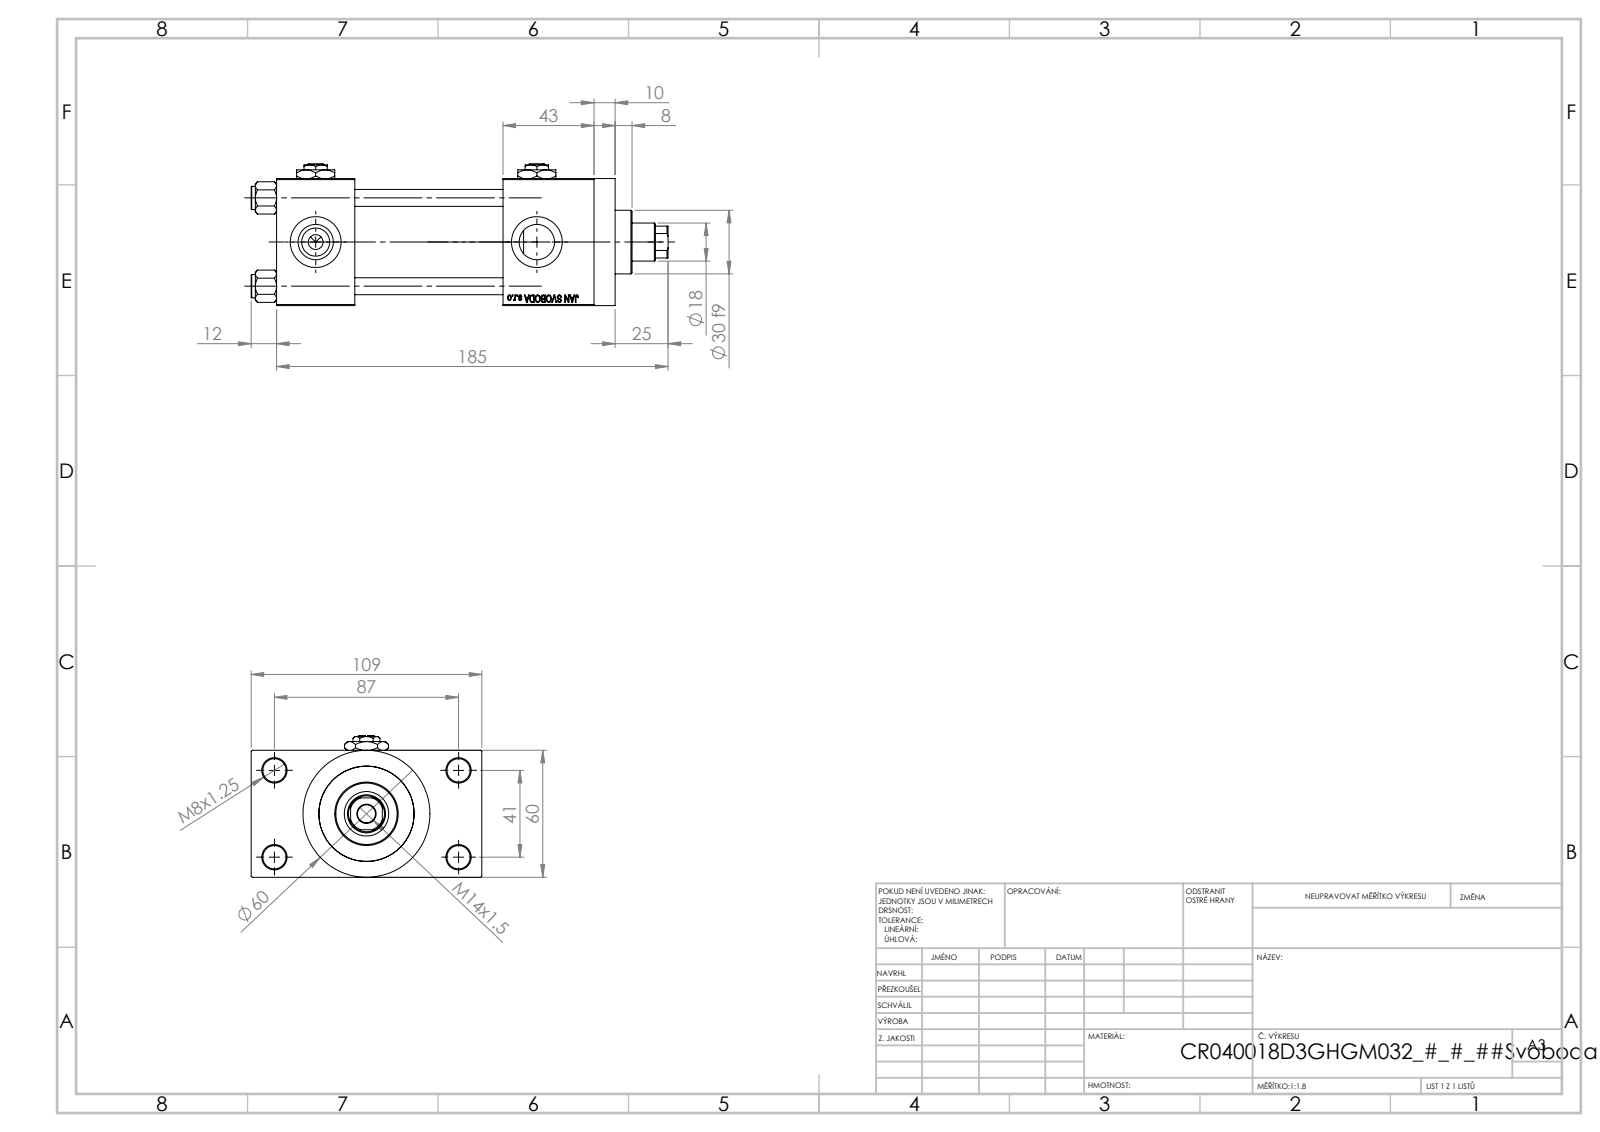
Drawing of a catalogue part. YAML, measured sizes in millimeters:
part_name: "V215_VC_A; NUT_M5_D; V215CR_D_TYCINKA; V215CR_VCP_D (+2 more)"
step_written_by: "SolidWorks 2019 (CONFIG_CONTROL_DESIGN)"
units: millimeters
bodies: {solids: 13, faces: 1205, planar: 546, cylindrical: 99, other: 560}
overall_size: [197, 109, 67]
volume: 520667
surface_area: 130319
round_holes:
  - {diameter: 8, count: 4}
  - {diameter: 11, count: 4}
  - {diameter: 16.66, count: 4}
  - {diameter: 24, count: 4}
  - {diameter: 7, count: 3}
  - {diameter: 8.5, count: 1}
  - {diameter: 18, count: 1}
  - {diameter: 21, count: 1}
  - {diameter: 31, count: 1}
  - {diameter: 40, count: 1}
  - {diameter: 45, count: 1}
round_bosses_or_shafts:
  - {diameter: 11, count: 4}
  - {diameter: 60, count: 1}
  - {diameter: 46, count: 1}
  - {diameter: 30, count: 1}
partial_cylinders:
  - {radius: 8.5, count: 1}
face_to_face_distances: [60, 70, 24.5, 84.5, 107, 37, 43, 150, 113, 10]
hole_center_spacings: [22.65, 29.49, 41.7, 47.15, 48.09, 64.35, 76.49, 41]
